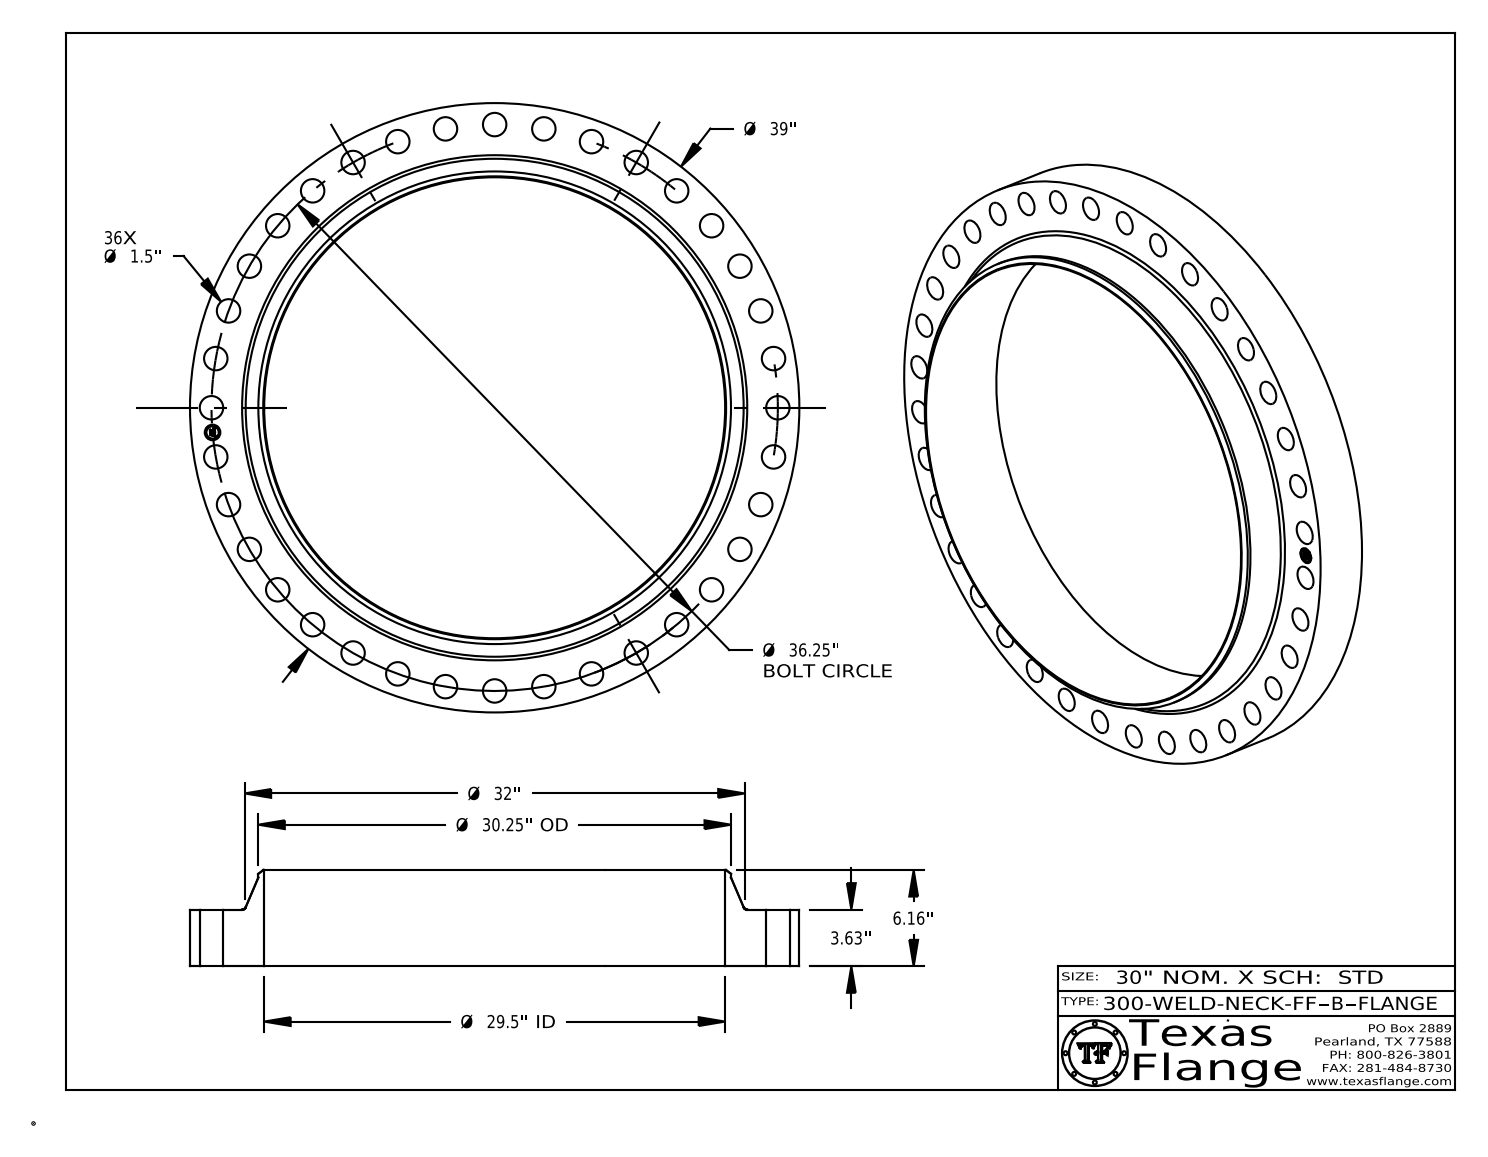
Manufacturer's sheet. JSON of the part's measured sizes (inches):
{"part_name": "300-WELD-NECK-FF, Series B", "step_written_by": "CATIA V5 STEP AP214 (AUTOMOTIVE_DESIGN)", "units": "inches", "bodies": {"solids": 1, "faces": 472, "planar": 368, "cylindrical": 98, "other": 6}, "overall_size": [39, 39, 6.16], "volume_in3": 1797, "surface_area_in2": 2686, "round_holes": [[1.5, 36], [1, 1], [29.5, 1]], "round_bosses_or_shafts": [[0.061, 8], [39, 1], [30.25, 1], [0.788, 1]], "face_to_face_distances": [3.63, 6.16, 2.53, 3.615, 0.015, 2.545, 0.298, 0.293, 0.019, 0.055], "hole_center_spacings": [18.125, 9.382, 27.769, 25.633, 35.699, 18.125, 36.112, 6.295]}
